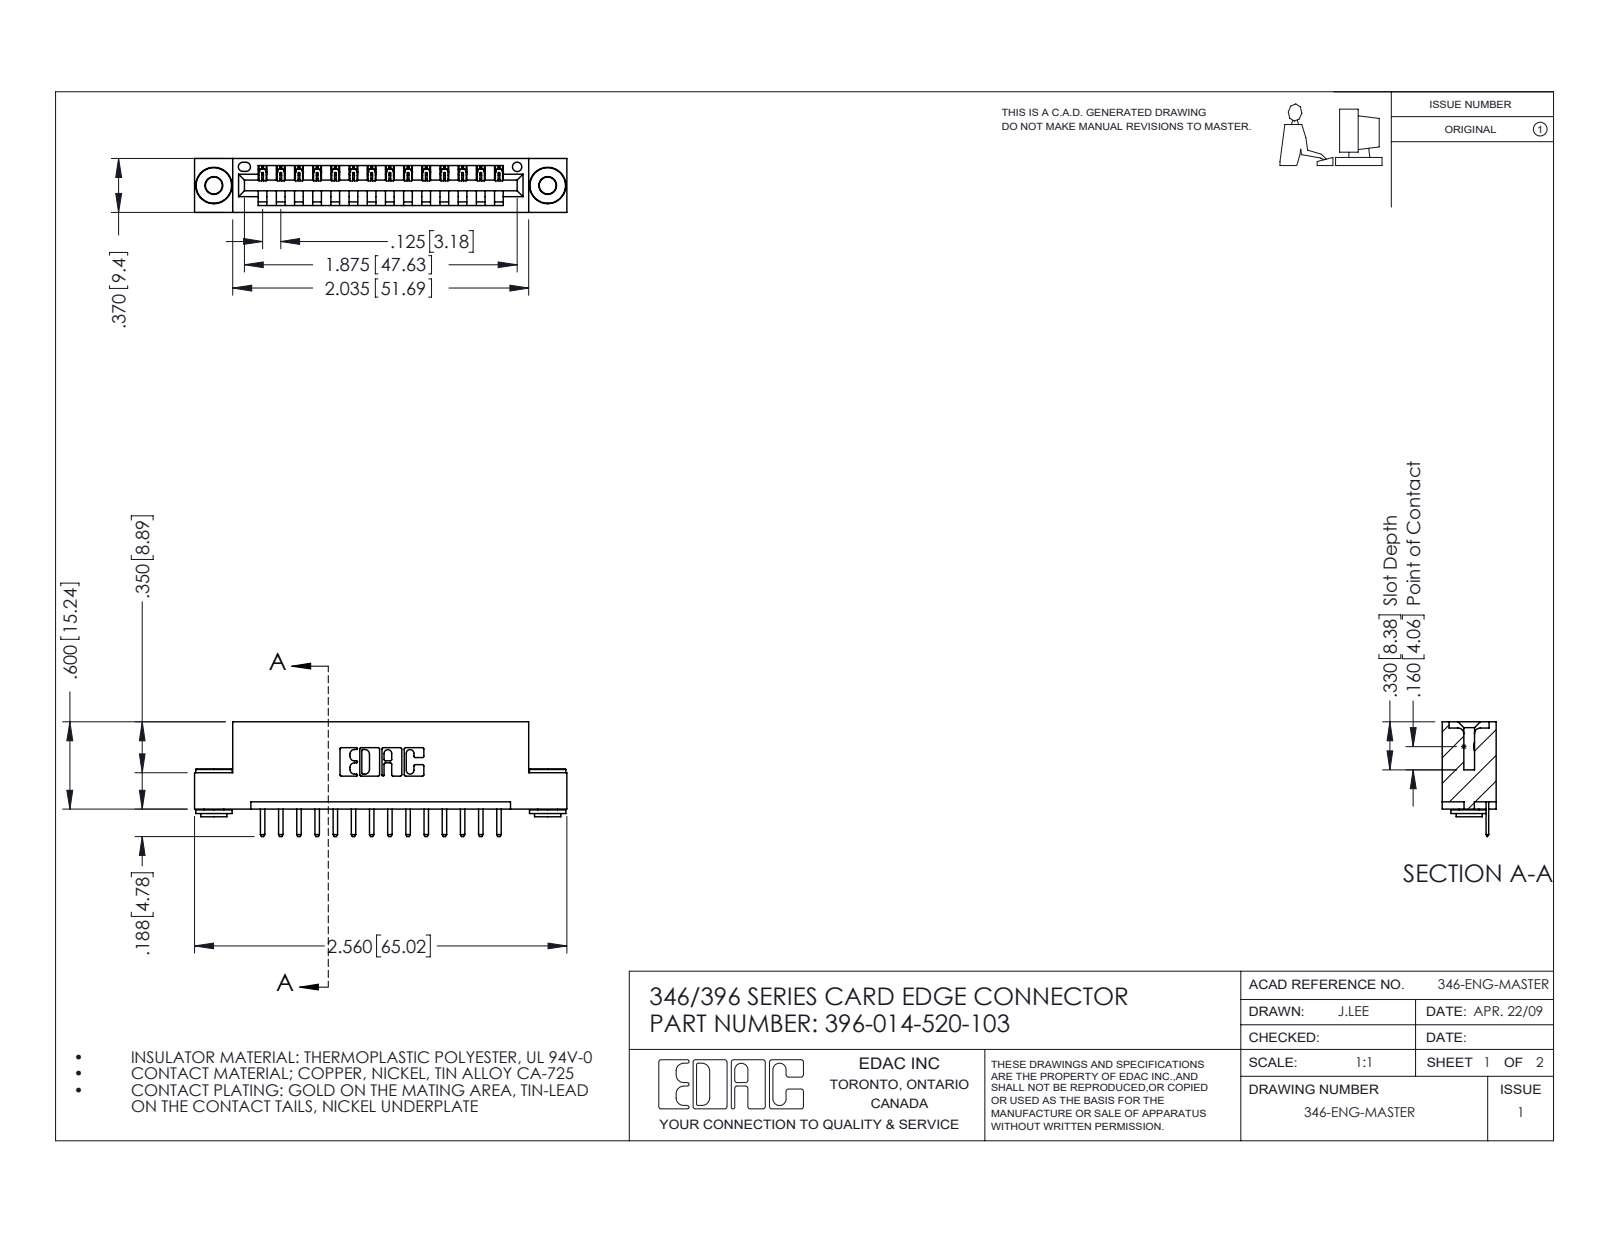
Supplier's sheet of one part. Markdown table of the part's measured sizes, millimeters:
| quantity | value |
| --- | --- |
| part name | 345-292-001_345-293-120; 346 Part_Flush Mounting Lugs - 0.156 Dia-TH; 396-014-520-103; 345-250-002_345-250-002-102 |
| STEP written by | SolidWorks 2016 (CONFIG_CONTROL_DESIGN) |
| units | millimeters |
| bodies | 17 solids, 1028 faces (674 planar, 346 cylindrical, 8 other) |
| overall size | 65 × 20 × 9.4 |
| volume | 6 010 mm³ |
| surface area | 7 297 mm² |
| round holes (diameter × count) | 2.9 × 2, 4 × 2, 1.6 × 1 |
| round bosses / shafts (diameter × count) | 6.4 × 2, 4.6 × 2, 3.5 × 2 |
| partial cylindrical surfaces (radius × count) | 0.3 × 30, 0.2 × 28, 0.3 × 22, 0.2 × 6, 0.8 × 6, 0.7 × 3, 0.8 × 2, 1 × 2 |
| main face-to-face distances | 6.4, 9.4, 1.2, 8.2, 3.8, 5.6, 2.5, 4.4, 0.6, 1.8 |
| hole center spacings | 6.2, 53.1, 58.3 |
